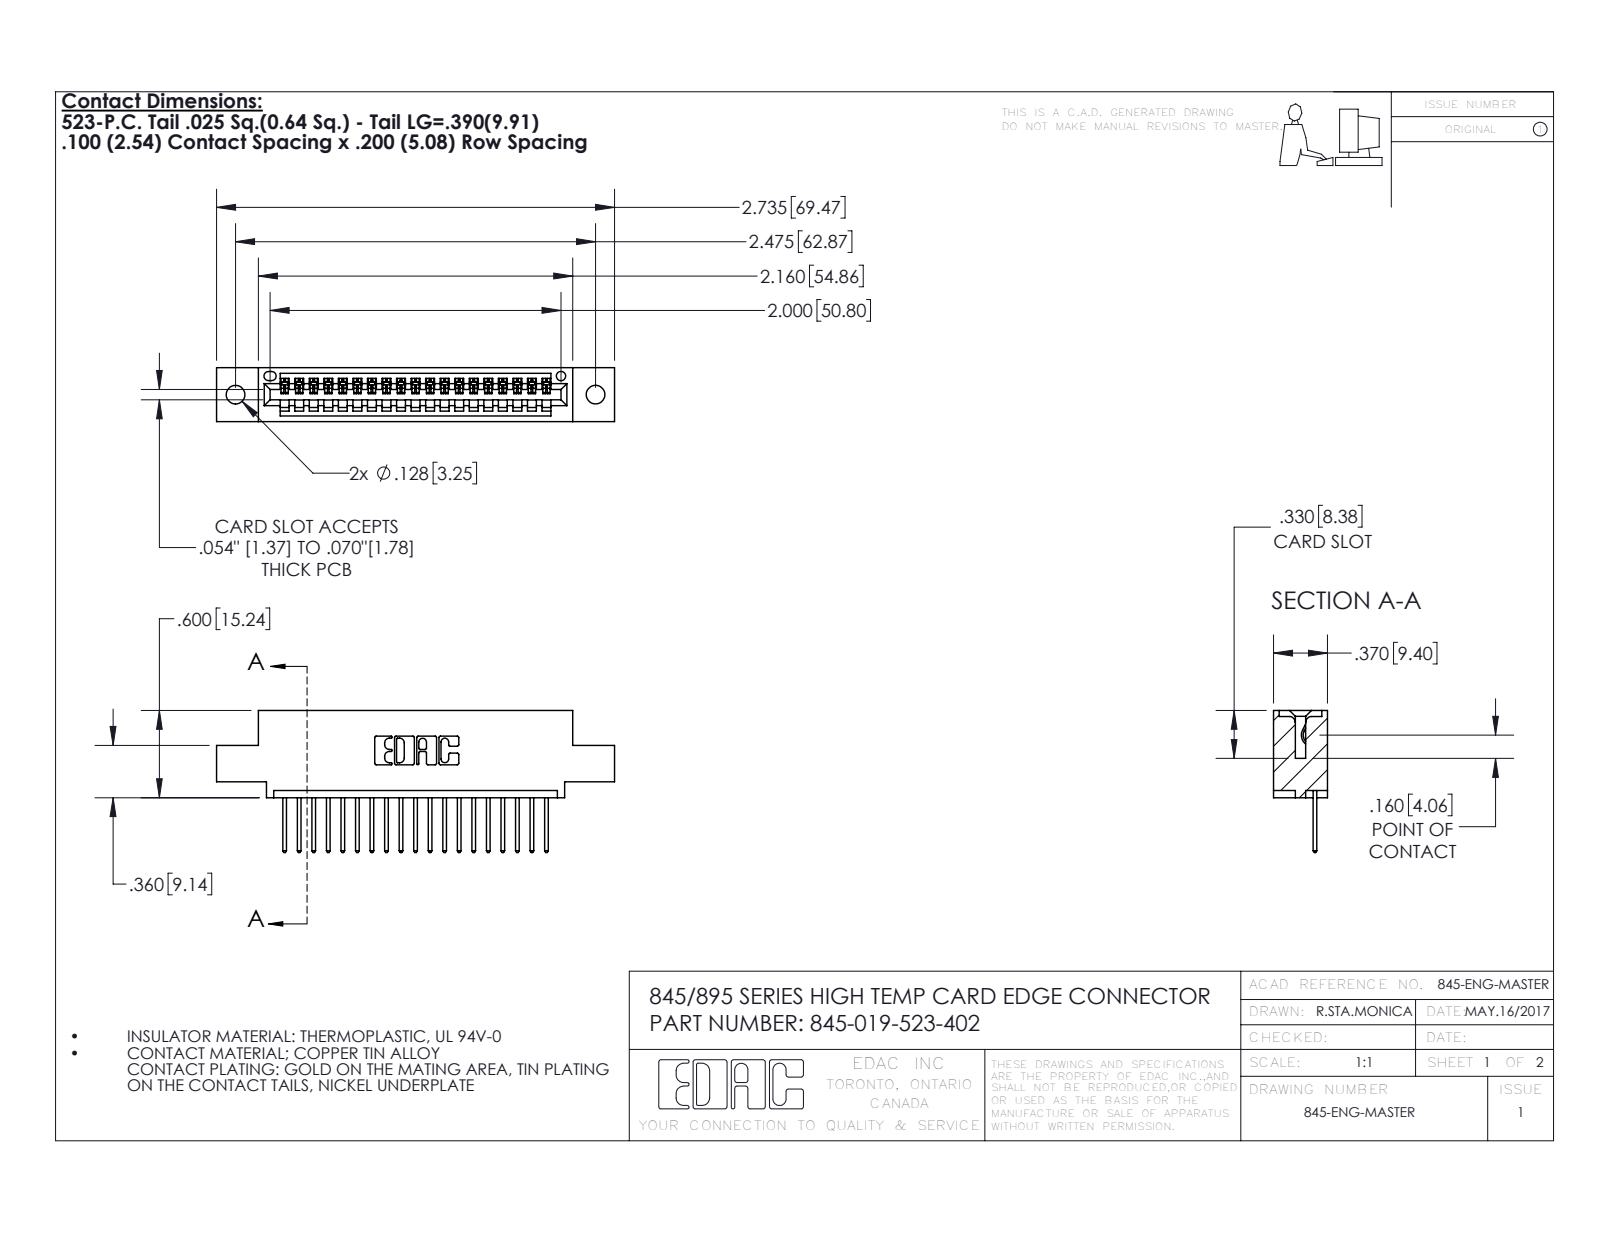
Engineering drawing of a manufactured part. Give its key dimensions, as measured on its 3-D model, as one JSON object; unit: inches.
{"part_name": "345 Part_0.110 Offset - 0.128 Dia; 345-019-523-402; 345-292-001_345-293-123", "step_written_by": "SolidWorks 2016 (CONFIG_CONTROL_DESIGN)", "units": "inches", "bodies": {"solids": 20, "faces": 1232, "planar": 844, "cylindrical": 388, "other": 0}, "overall_size": [2.735, 0.977, 0.37], "volume_in3": 0.384, "surface_area_in2": 12.21, "round_holes": [[0.128, 2], [0.064, 1]], "partial_cylinders_radius": [[0.006, 38], [0.01, 38], [0.01, 22], [0.007, 6], [0.031, 6], [0.026, 3], [0.031, 2], [0.04, 2]], "face_to_face_distances": [0.298, 0.072, 0.37, 0.2, 0.098, 0.272, 0.025, 0.225, 0.149, 0.6], "hole_center_spacings": [0.27, 2.241, 2.475]}
